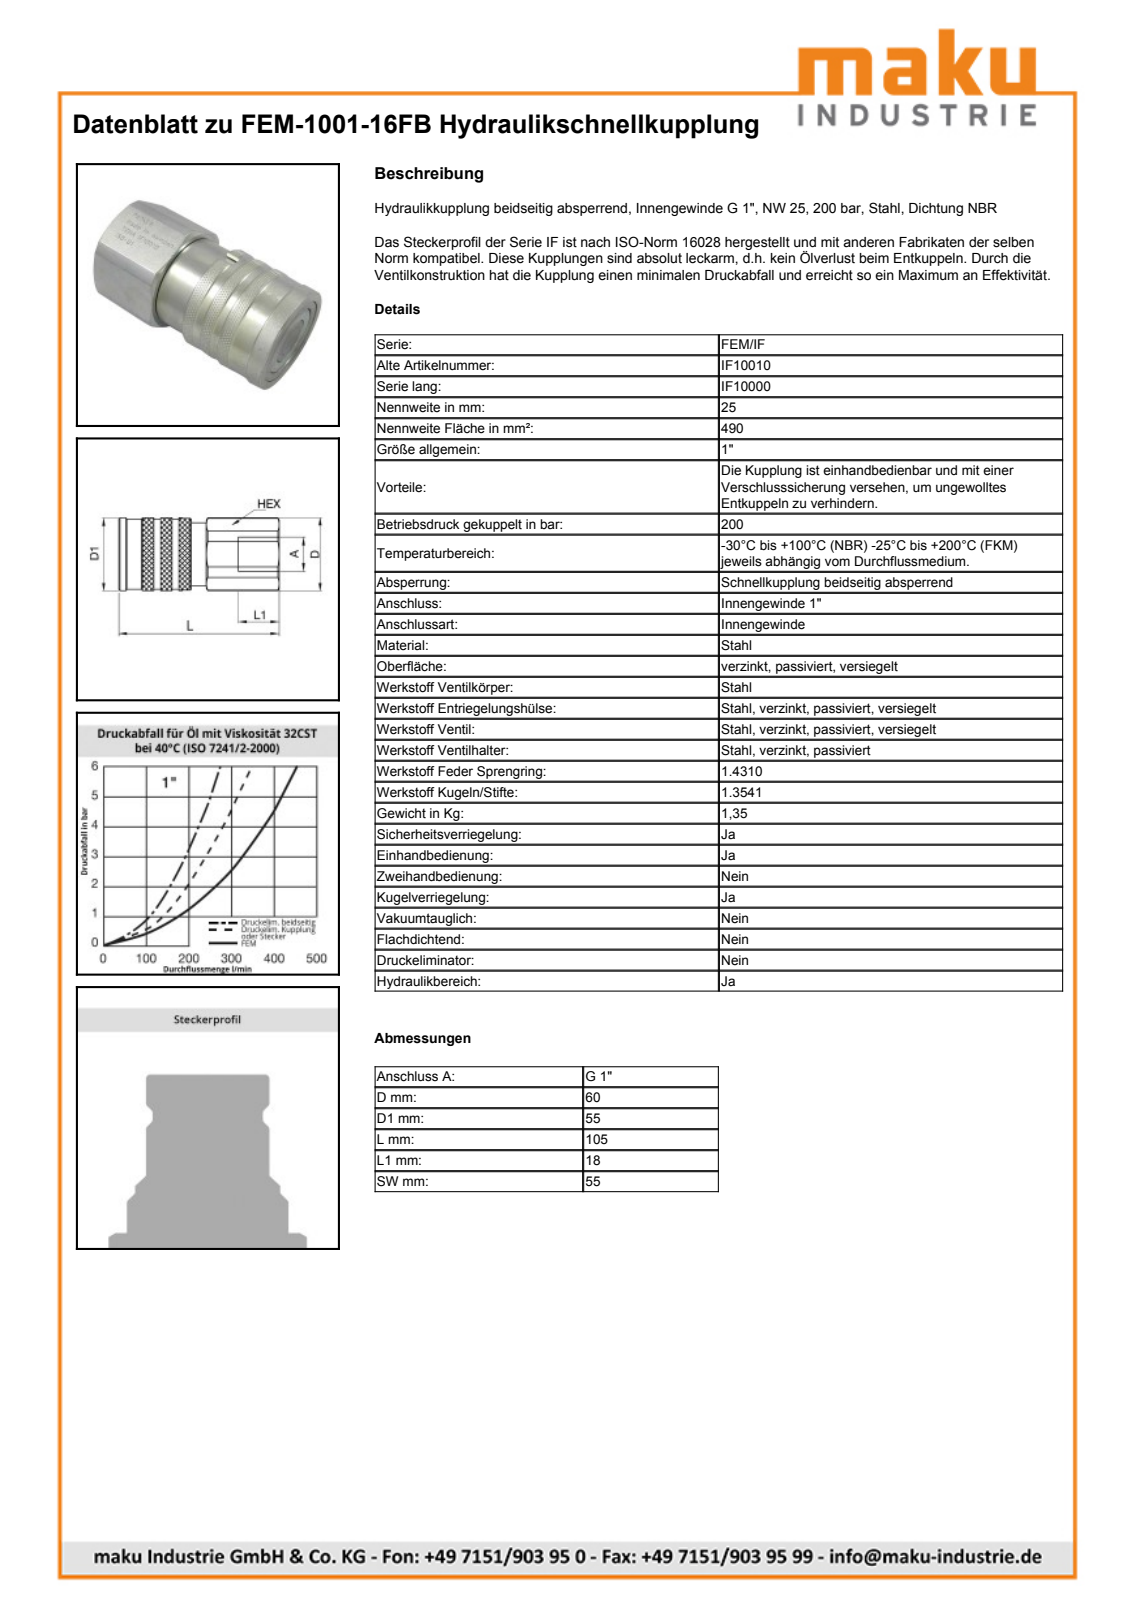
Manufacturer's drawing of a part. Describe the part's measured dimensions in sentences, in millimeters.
The part is named "FEM-1001-16FB". Its 3-D file was written by "SolidWorks 2009 (AUTOMOTIVE_DESIGN)". It is 1 solid with 113 faces: 31 planar, 44 cylindrical and 38 other. Overall it measures 105 by 60 by 55 millimeters. Its volume is 230 956 cubic millimeters and its surface area 29 656 square millimeters. Round holes: 1 of diameter 3, 1 of diameter 23.7, 1 of diameter 30.3, 1 of diameter 36.1, 1 of diameter 45.35, 1 of diameter 50.3. Round bosses or shafts: 1 of diameter 55, 1 of diameter 54, 1 of diameter 49.6, 1 of diameter 45.15, 1 of diameter 35.9. Partial cylindrical surfaces (rounded edges, fillets, slot ends): 2 of radius 0.6, 1 of radius 23.45, 1 of radius 30. The main face-to-face distances are 55, 21.57, 40, 64.93, 104.93, 83.36, 104.49, 82.92, 0.44, 18.43.
